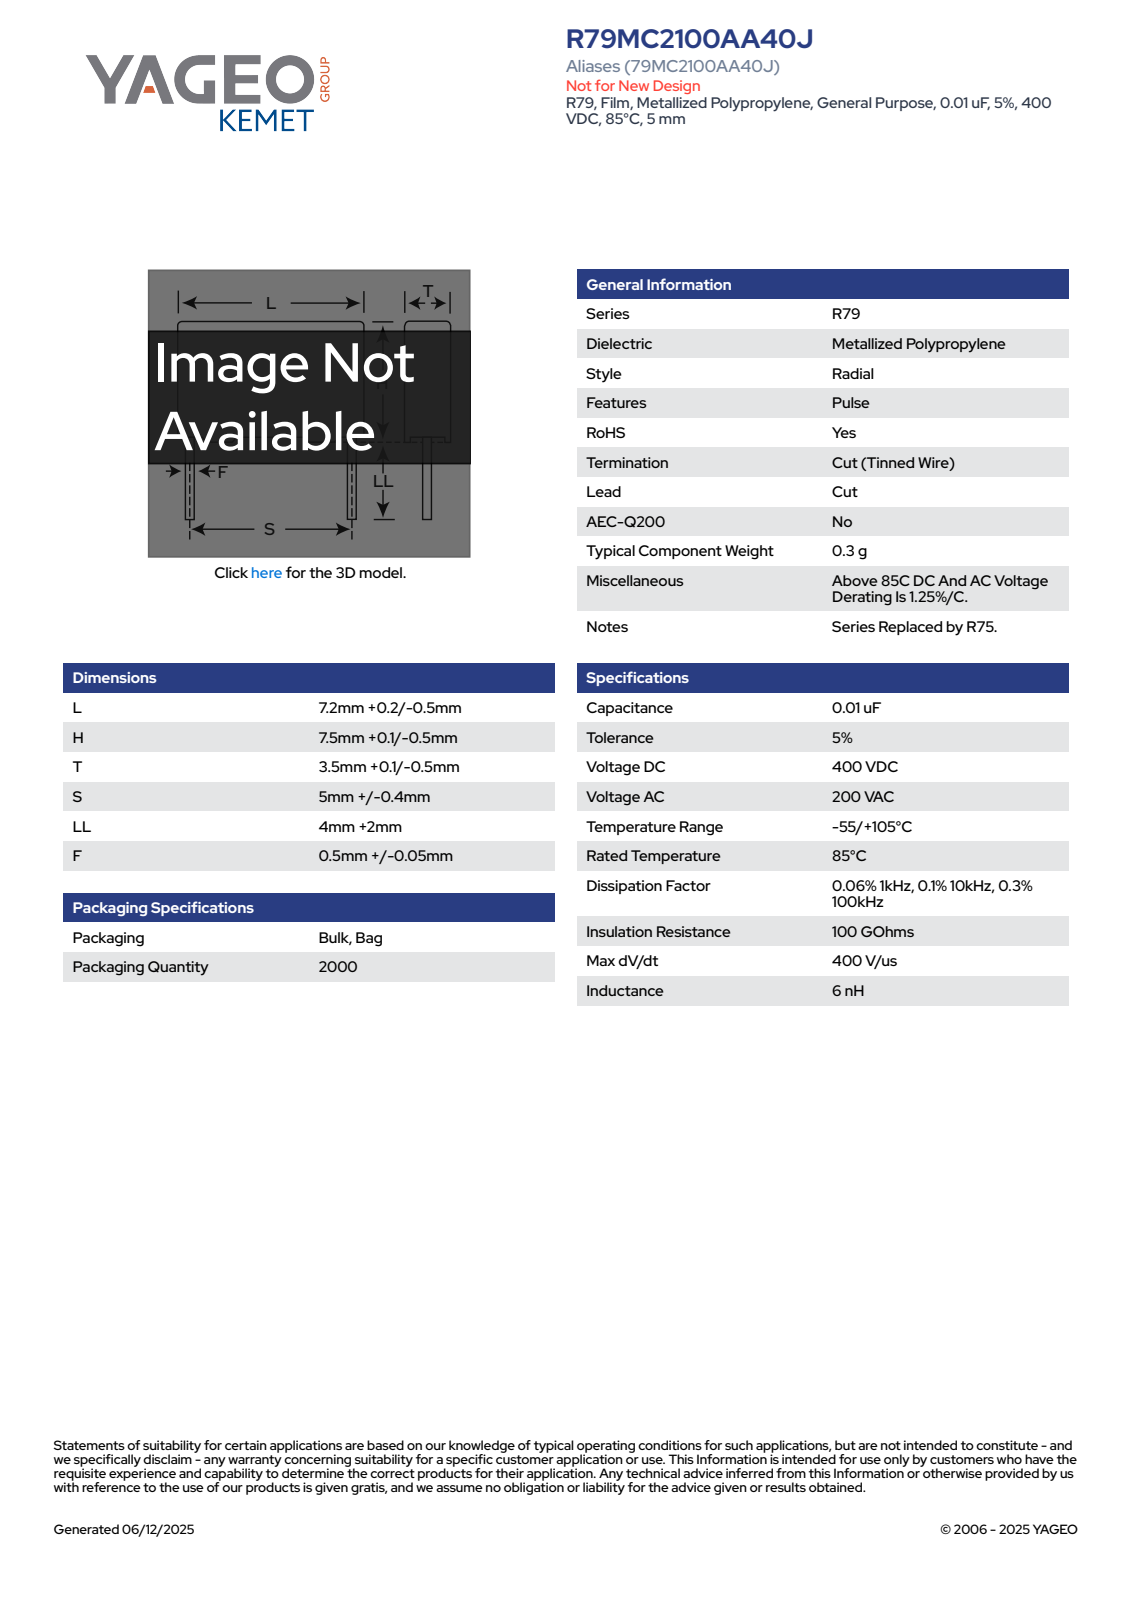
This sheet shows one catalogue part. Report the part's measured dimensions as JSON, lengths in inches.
{"part_name": "CFR_RB2_7.2X7.5X3.5_L7.4H7.6T3.6S5LL6F0.55", "step_written_by": "SolidWorks 2014 (AUTOMOTIVE_DESIGN)", "units": "inches", "bodies": {"solids": 4, "faces": 85, "planar": 77, "cylindrical": 8, "other": 0}, "overall_size": [0.535, 0.291, 0.142], "volume_in3": 0.011, "surface_area_in2": 0.397, "round_bosses_or_shafts": [[0.022, 2]], "partial_cylinders_radius": [[0.02, 4]], "face_to_face_distances": [0.142, 0.291, 0.27, 0.132, 0.122, 0.281, 0.03, 0.299, 0.272, 0.019]}
